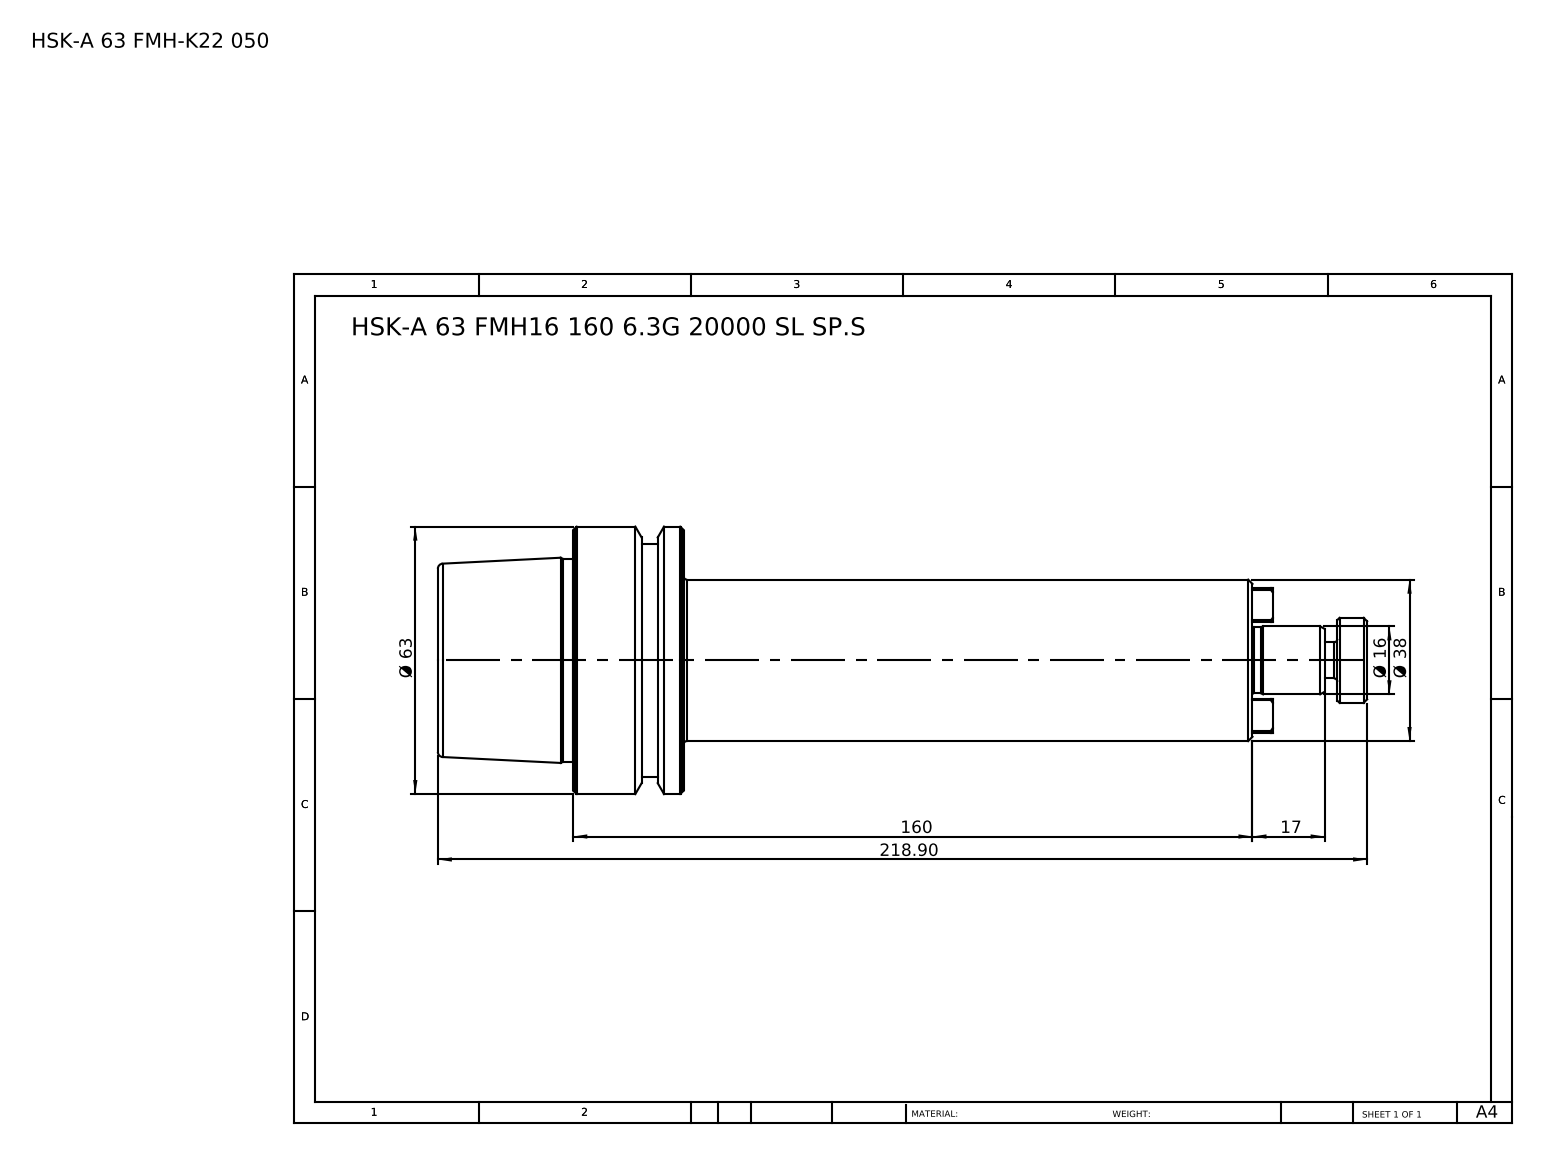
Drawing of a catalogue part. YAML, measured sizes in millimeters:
part_name: "HSK-A 63 FMH16 160 6.3G 20000 SL SP.S"
step_written_by: "SolidWorks 2014 (CONFIG_CONTROL_DESIGN)"
units: millimeters
bodies: {solids: 1, faces: 99, planar: 37, cylindrical: 18, other: 44}
overall_size: [218.9, 63, 63]
volume: 290822
surface_area: 34650
round_bosses_or_shafts:
  - {diameter: 63, count: 1}
  - {diameter: 55, count: 1}
  - {diameter: 47.78, count: 1}
  - {diameter: 38, count: 1}
  - {diameter: 20, count: 1}
  - {diameter: 16, count: 1}
  - {diameter: 15.6, count: 1}
  - {diameter: 8.5, count: 1}
face_to_face_distances: [57.9, 26, 31.9, 134, 160, 191.9, 27, 161, 187, 218.9]
